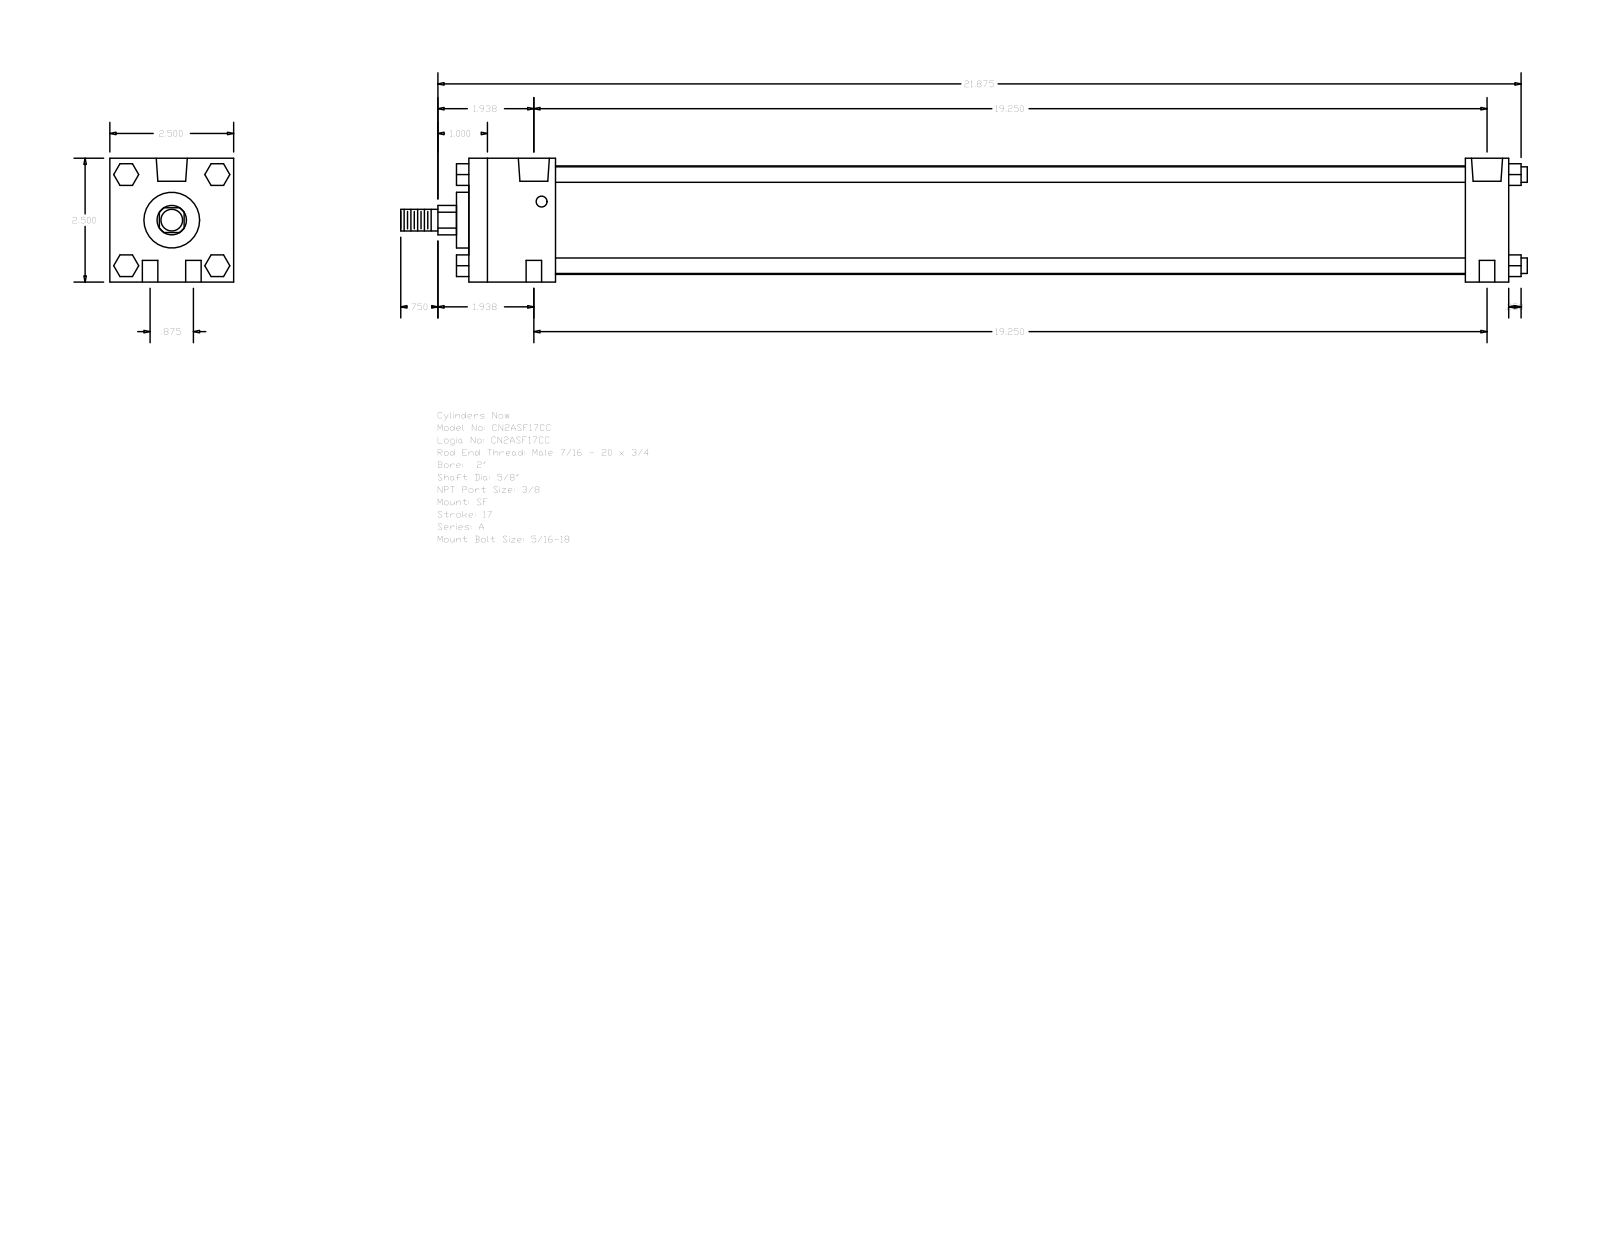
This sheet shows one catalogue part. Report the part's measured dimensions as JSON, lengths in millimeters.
{"part_name": "A_SF__0200_0.625", "step_written_by": "GSSL Pune (CONFIG_CONTROL_DESIGN)", "units": "millimeters", "bodies": {"solids": 0, "faces": 124, "planar": 94, "cylindrical": 30, "other": 0}, "overall_size": [577.85, 63.5, 63.5], "round_holes": [[7.94, 4], [5.56, 2], [15.93, 2]], "round_bosses_or_shafts": [[7.94, 4], [55.63, 1], [28.57, 1], [15.88, 1], [11.11, 1]], "partial_cylinders_radius": [[7.54, 1]], "face_to_face_distances": [63.5, 533.39, 511.17, 22.22, 44.45, 466.72, 488.94, 6.35, 539.74, 50.8], "hole_center_spacings": [11.11, 489.08, 488.95, 22.22, 489.45, 481]}
